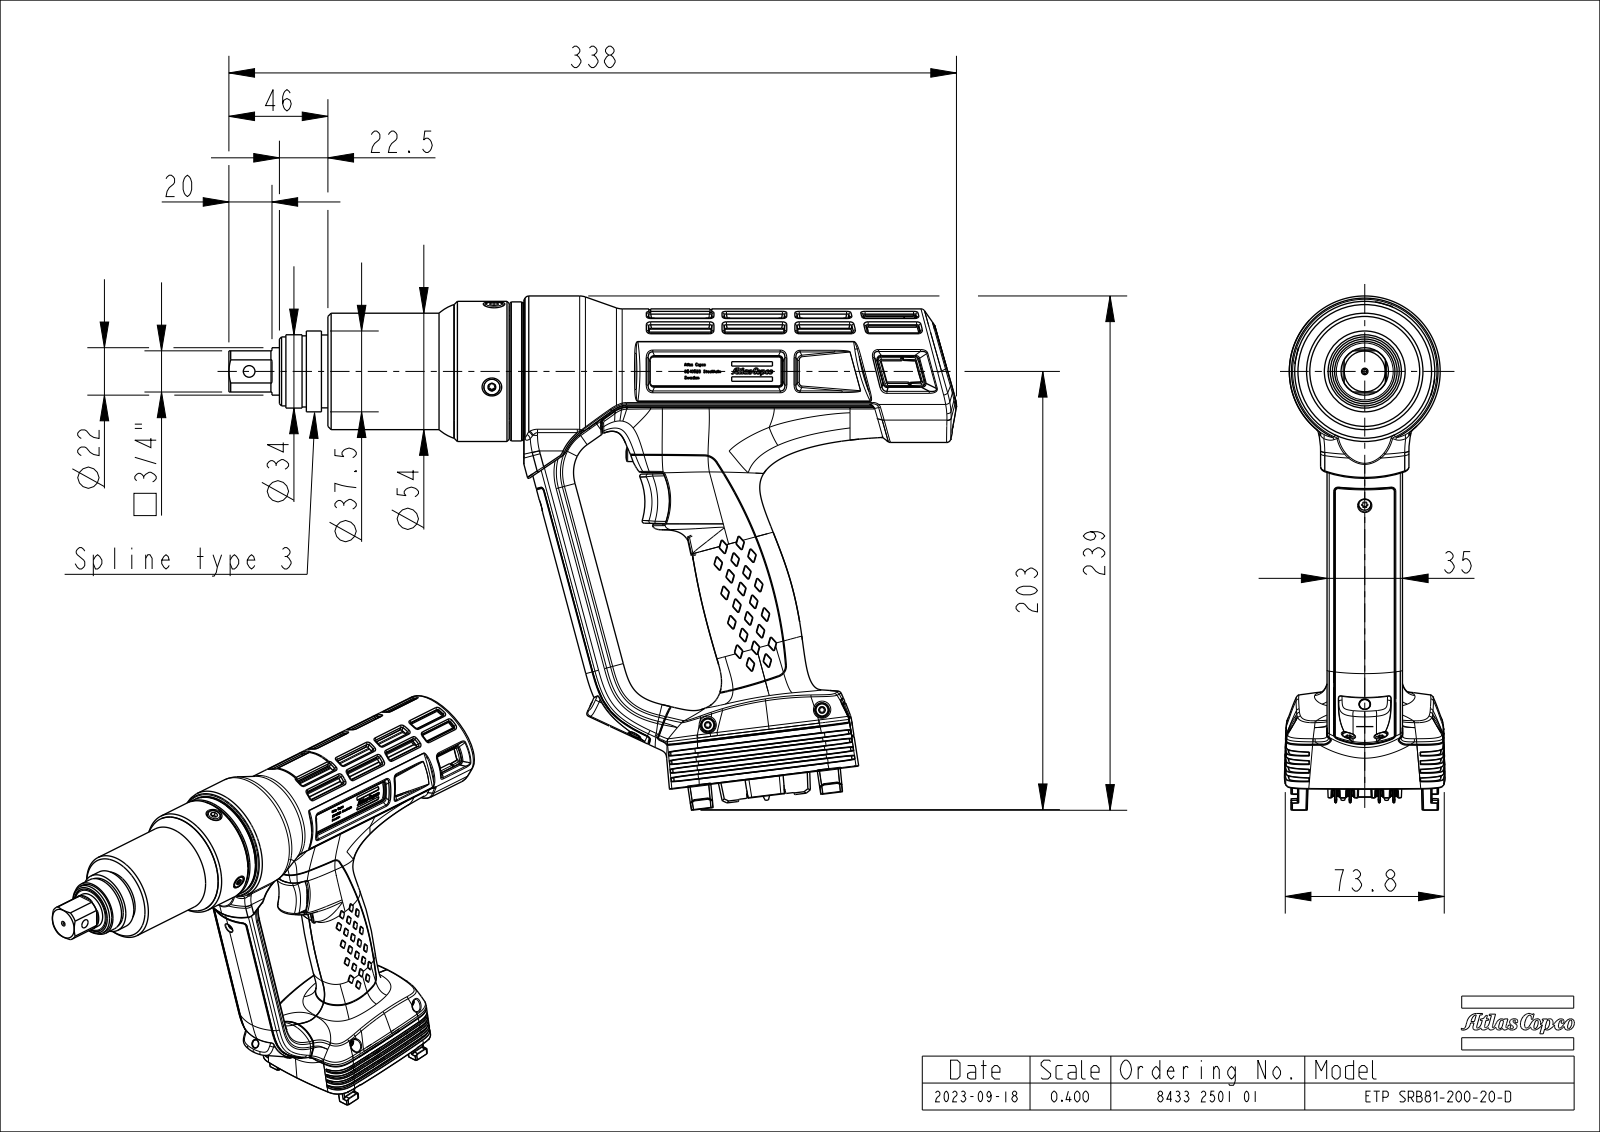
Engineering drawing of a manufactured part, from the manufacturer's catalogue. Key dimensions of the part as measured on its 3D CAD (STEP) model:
Part name (STEP PRODUCT): EXT_COMP_SW0002
STEP written by: CREO PARAMETRIC BY PTC INC, 2018100 (CONFIG_CONTROL_DESIGN)
Units: inches
Bodies: 4 solids, 7929 faces (2839 planar, 1481 cylindrical, 3609 other)
Overall size (bounding box): 13.293 × 9.256 × 2.935
Volume: 70.6 in³ · Surface area: 314.3 in²
Round holes (diameter × count): ⌀0.118 ×3, ⌀0.138 ×2, ⌀0.161 ×2, ⌀0.079 ×1, ⌀0.213 ×1, ⌀0.394 ×1
Round bosses / shafts (diameter × count): ⌀0.295 ×2, ⌀0.22 ×2, ⌀0.157 ×2, ⌀2.559 ×1, ⌀2.52 ×1, ⌀2.48 ×1, ⌀2.315 ×1, ⌀2.126 ×1
Partial cylindrical surfaces — rounded edges, fillets, slot ends (radius × count): R0.012 ×411, R0.02 ×252, R0.039 ×40, R0.02 ×36, R0.011 ×34, R0.004 ×32, R0.031 ×22, R0.079 ×19
Main face-to-face distances: 0.217, 0.039, 0.797, 0.266, 1.541, 3.78, 3.563, 0.531, 0.197, 0.404
Hole centre spacings: 0.89
